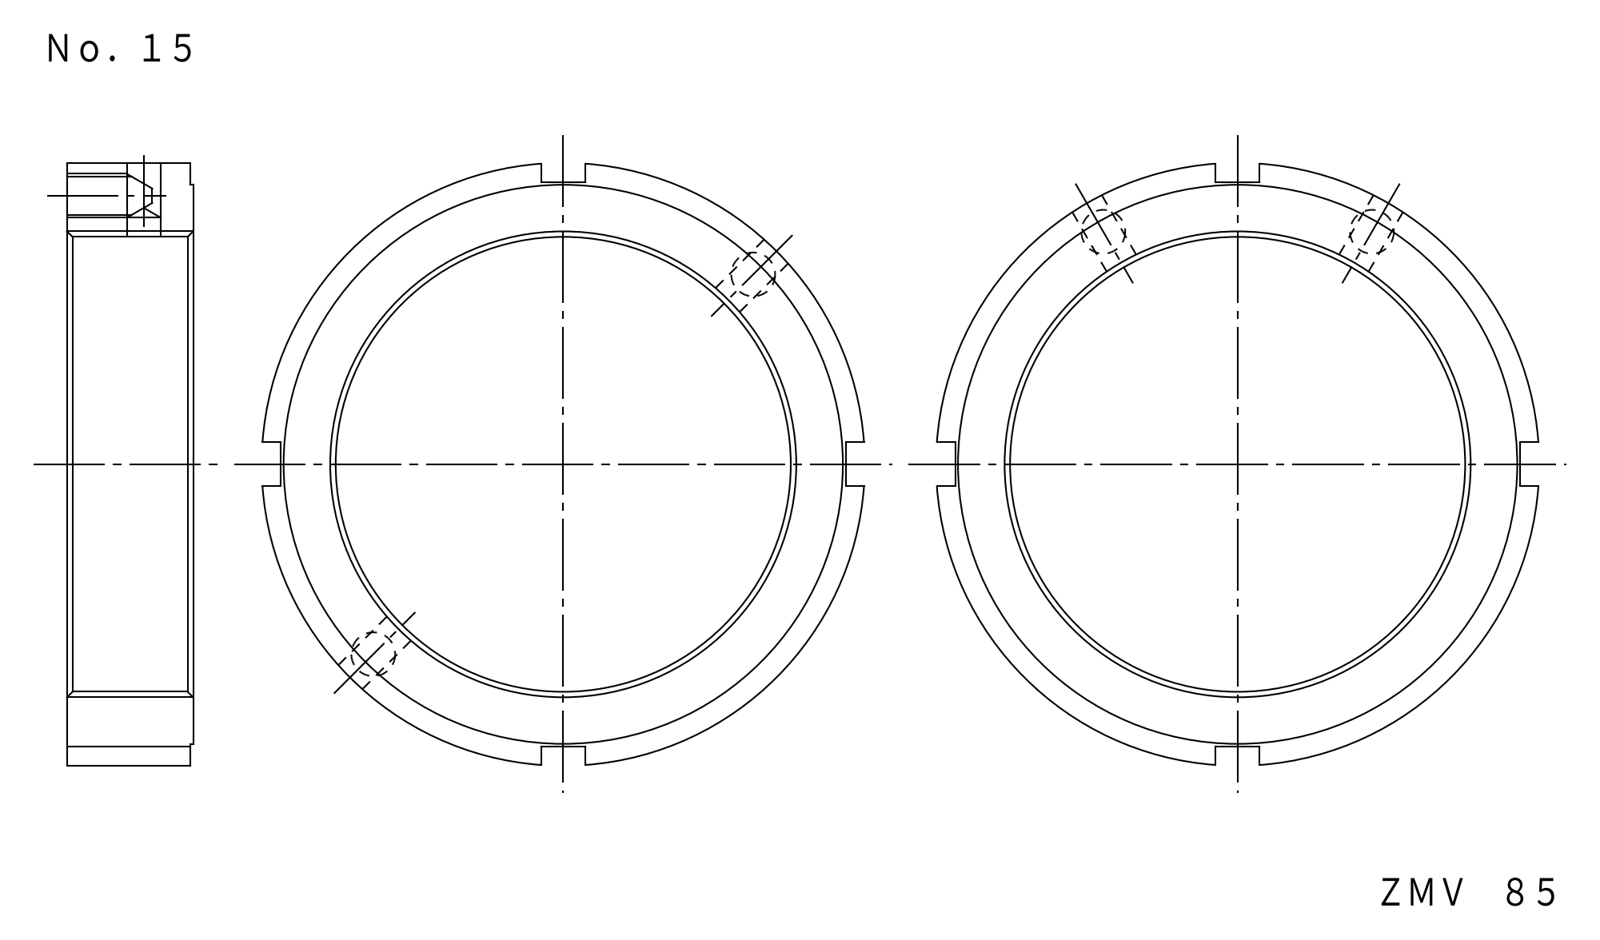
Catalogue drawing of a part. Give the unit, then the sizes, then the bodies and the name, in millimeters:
Units: millimetres
Overall size (bounding box): 109.71 × 109.71 × 23
Round holes (diameter × count): ⌀6.2 ×2, ⌀6.65 ×2, ⌀85 ×1
Round bosses / shafts (diameter × count): ⌀110 ×1, ⌀102 ×1
Main face-to-face distances: 23, 0.5, 22.5, 47.5, 55.5, 103, 8
Hole centre spacings: 49, 98
Volume: 83 360 mm³ · Surface area: 22 836 mm²
Bodies: 1 solid, 29 faces (15 planar, 10 cylindrical, 4 other)
Part name (STEP PRODUCT): FKD ZMV85
STEP written by: Autodesk Inventor LT (CONFIG_CONTROL_DESIGN)
